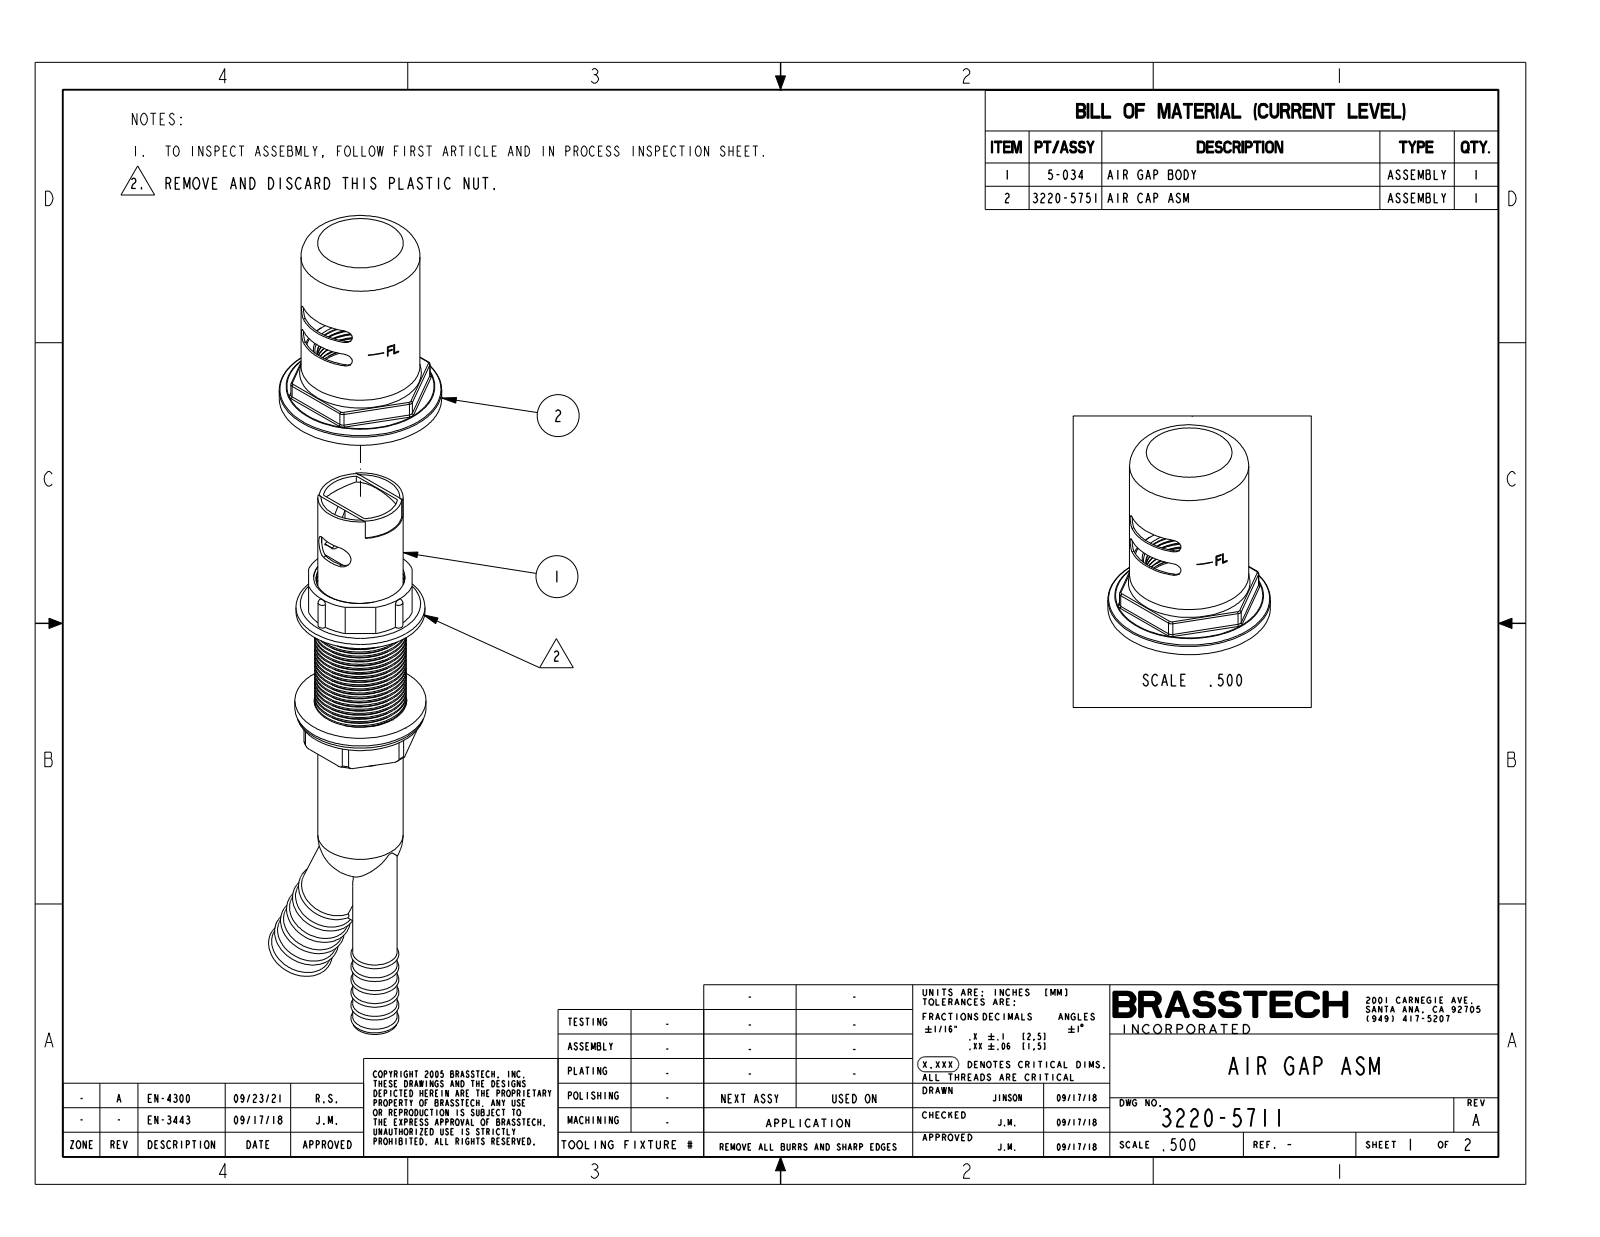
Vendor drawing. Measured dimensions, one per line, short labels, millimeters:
name: 3220-5711
written by: CREO PARAMETRIC BY PTC INC, 2018400 (AUTOMOTIVE_DESIGN)
unit: mm
bodies: 2 solids, 310 faces (73 planar, 146 cylindrical, 91 other)
size: 223.6 × 68.5 × 56.6
volume: 167 600 mm³; area: 52 350 mm²
holes: 1× ⌀30.5, 1× ⌀32.3, 1× ⌀32.5, 1× ⌀40
bosses: 1× ⌀56.6, 1× ⌀45.7, 1× ⌀44.7, 1× ⌀41.5, 1× ⌀32, 1× ⌀29.7, 1× ⌀21.7, 1× ⌀15.5
rounds: 12× R0.5, 6× R1, 6× R1.5, 4× R2.5, 2× R4, 1× R20.5
face distances: 23.4, 10.8, 34.2, 89, 89.8, 65.7, 66.4, 54.9, 55.6, 0.8
